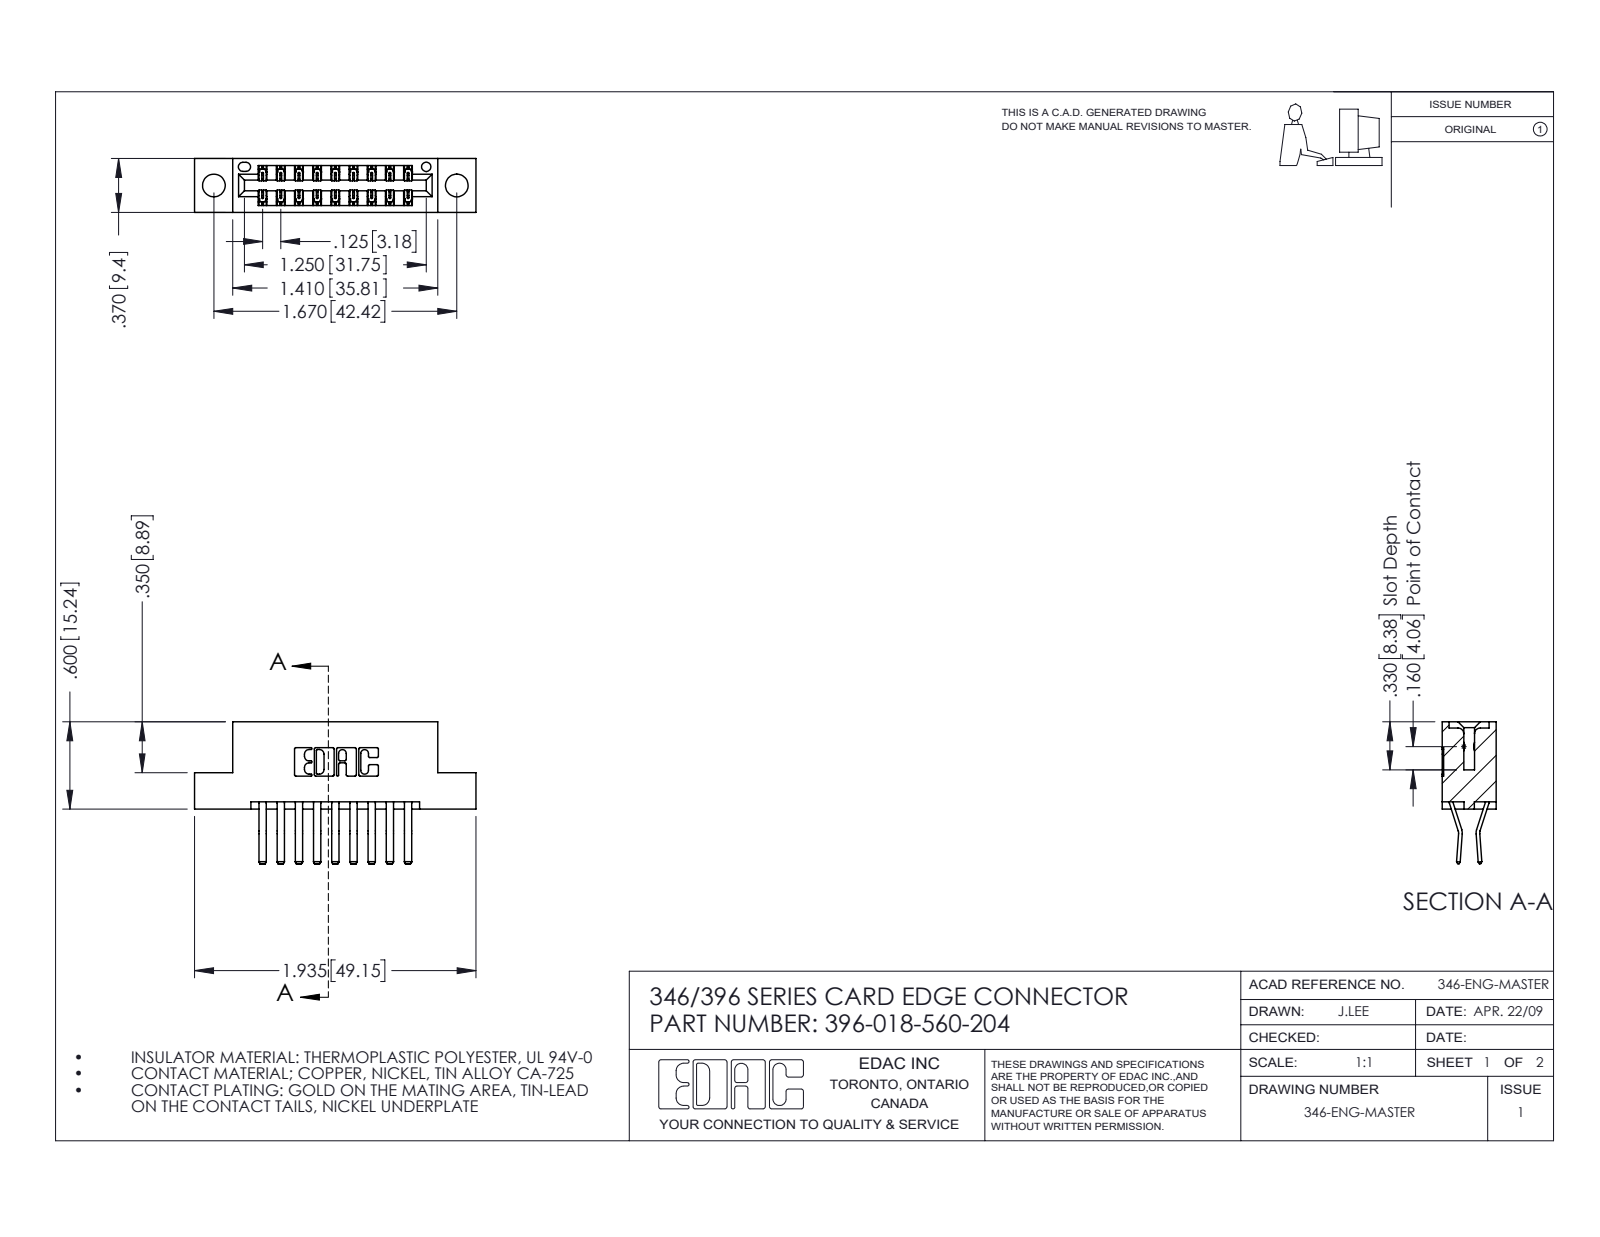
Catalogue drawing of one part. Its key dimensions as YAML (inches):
part_name: "396-018-560-204; 346 Part_Flush Mounting Lugs - 0.156 Dia-TH; 345-292-001_560 Tail"
step_written_by: "SolidWorks 2016 (CONFIG_CONTROL_DESIGN)"
units: inches
bodies: {solids: 19, faces: 1094, planar: 706, cylindrical: 388, other: 0}
overall_size: [1.935, 0.975, 0.37]
volume: 0.279
surface_area: 9.124
round_holes:
  - {diameter: 0.156, count: 2}
  - {diameter: 0.064, count: 1}
partial_cylinders:
  - {radius: 0.006, count: 27}
  - {radius: 0.01, count: 22}
  - {radius: 0.007, count: 6}
  - {radius: 0.031, count: 6}
  - {radius: 0.026, count: 3}
  - {radius: 0.01, count: 2}
  - {radius: 0.014, count: 2}
  - {radius: 0.022, count: 2}
face_to_face_distances: [0.25, 0.048, 0.322, 0.37, 0.025, 0.072, 0.298, 0.148, 0.222, 0.1]
hole_center_spacings: [0.246, 1.465, 1.67]
